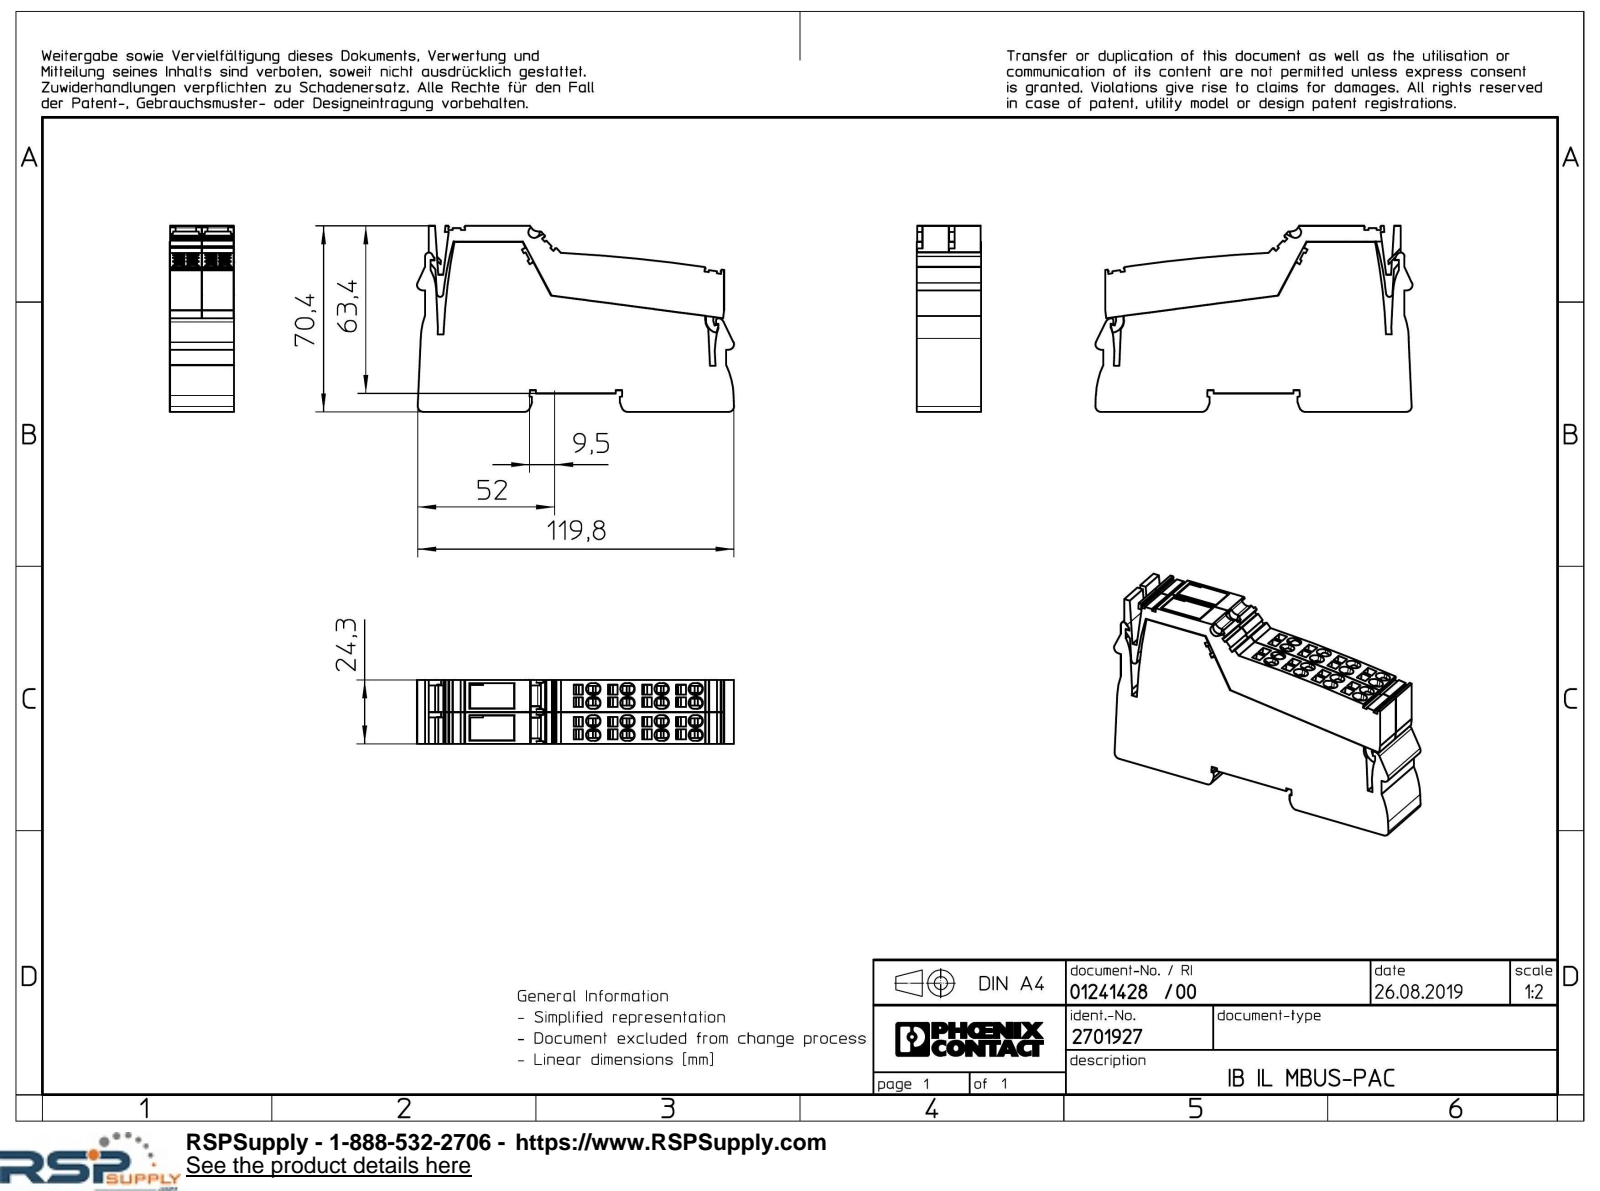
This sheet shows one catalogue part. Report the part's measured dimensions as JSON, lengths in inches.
{"part_name": "L-L_ST_GN_6021-select; L_L_4_GEH_GN_6021-select; L_L_LWL_OG_HKS_7K_AUSSEN-select.2; IB_IL_MBUS_PAC-select", "step_written_by": "Creo Elements/Direct Modeling 20.1A 29-Sep-2018 (C) Parametric Technology GmbH (AUTOMOTIVE_DESIGN)", "units": "inches", "bodies": {"solids": 5, "faces": 1106, "planar": 950, "cylindrical": 100, "other": 56}, "overall_size": [4.729, 2.773, 0.957], "volume_in3": 9.739, "surface_area_in2": 73.12, "round_holes": [[0.047, 12]], "partial_cylinders_radius": [[0.089, 32], [0.079, 6], [0.024, 4], [0.006, 2], [0.335, 2], [0.374, 2], [0.657, 2], [1.181, 2]], "face_to_face_distances": [0.957, 0.478, 0.472, 0.48, 0.955, 0.476, 0.482, 0.953, 0.474, 0.951], "hole_center_spacings": [0.512, 0.546, 0.701, 0.189, 0.478, 0.588, 0.841, 1.024]}
